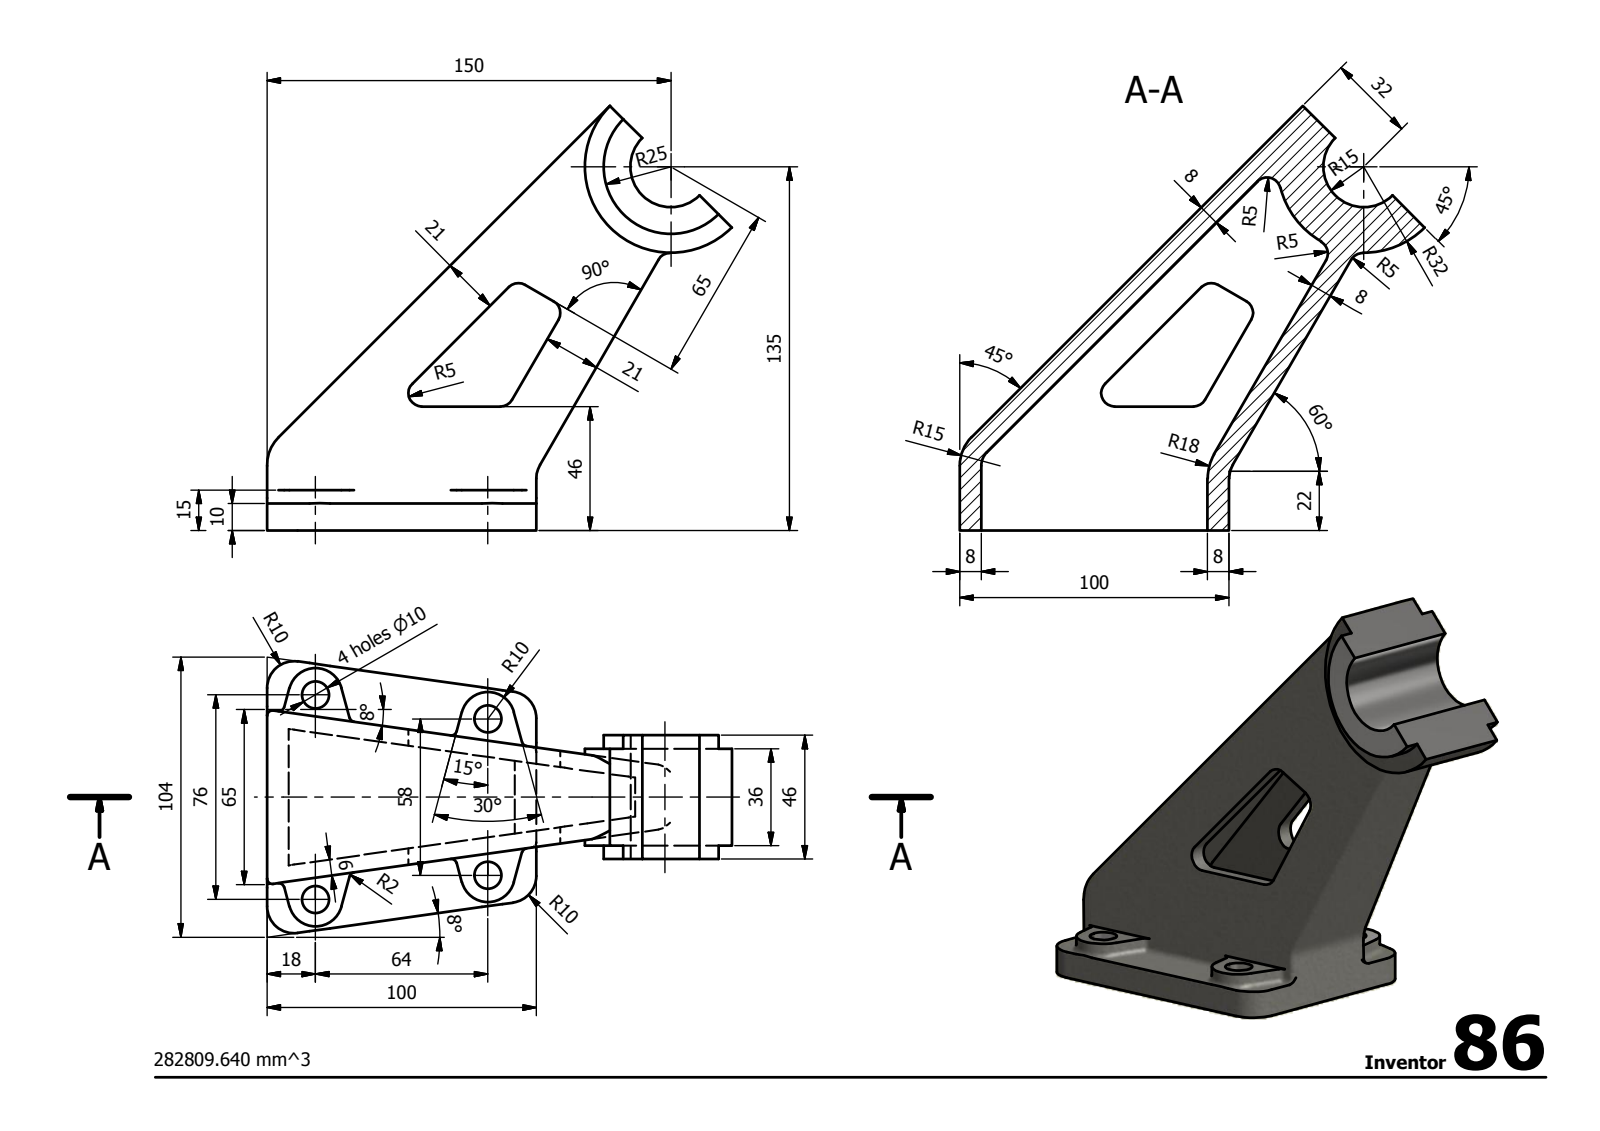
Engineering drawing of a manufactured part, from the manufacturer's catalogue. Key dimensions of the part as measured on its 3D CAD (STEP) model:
STEP written by: Autodesk Inventor 2014 (AUTOMOTIVE_DESIGN)
Units: millimetres
Bodies: 1 solid, 131 faces (47 planar, 62 cylindrical, 22 other)
Overall size (bounding box): 172.63 × 157.63 × 100.99
Volume: 282 818 mm³ · Surface area: 77 938 mm²
Round holes (diameter × count): ⌀10 ×4
Partial cylindrical surfaces — rounded edges, fillets, slot ends (radius × count): R2 ×26, R10 ×9, R5 ×7, R15 ×2, R7 ×1, R18 ×1, R25 ×1, R32 ×1
Main face-to-face distances: 5.99, 8, 5, 10, 92, 41, 15, 21, 13, 46
Hole centre spacings: 64.63, 92.66, 58, 76
